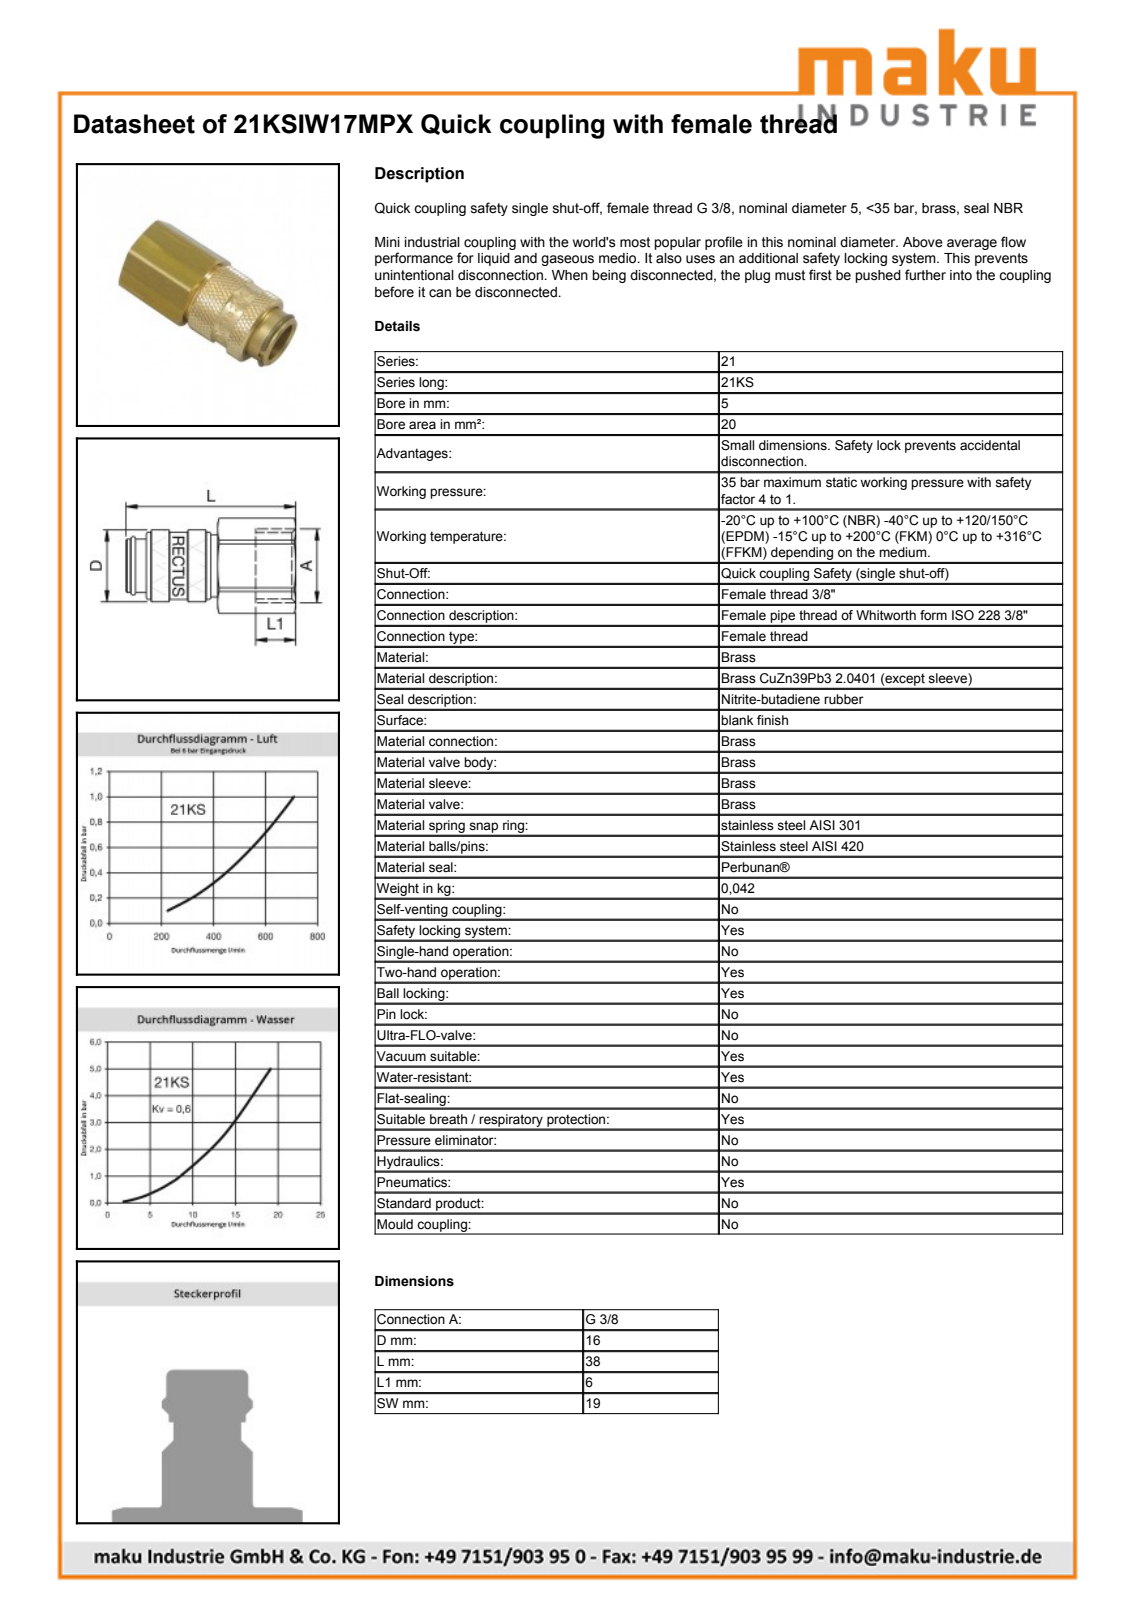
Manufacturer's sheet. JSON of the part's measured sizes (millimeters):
{"part_name": "D105596", "step_written_by": "Autodesk Inventor 2011 (AUTOMOTIVE_DESIGN)", "units": "millimeters", "bodies": {"solids": 2, "faces": 414, "planar": 147, "cylindrical": 57, "other": 210}, "overall_size": [38.15, 21.39, 19.62], "volume_mm3": 7043, "surface_area_mm2": 4358, "round_holes": [[7.5, 1], [12.25, 1], [12.8, 1], [14, 1], [14.95, 1]], "round_bosses_or_shafts": [[16.15, 1], [15.1, 1], [15, 1], [12, 1], [11.15, 1]], "partial_cylinders_radius": [[5.75, 1], [7.4, 1], [10.7, 1]], "face_to_face_distances": [19, 8.55, 20.6, 29.15, 38.15, 17.55, 9, 8.53, 29.13, 9.02]}
